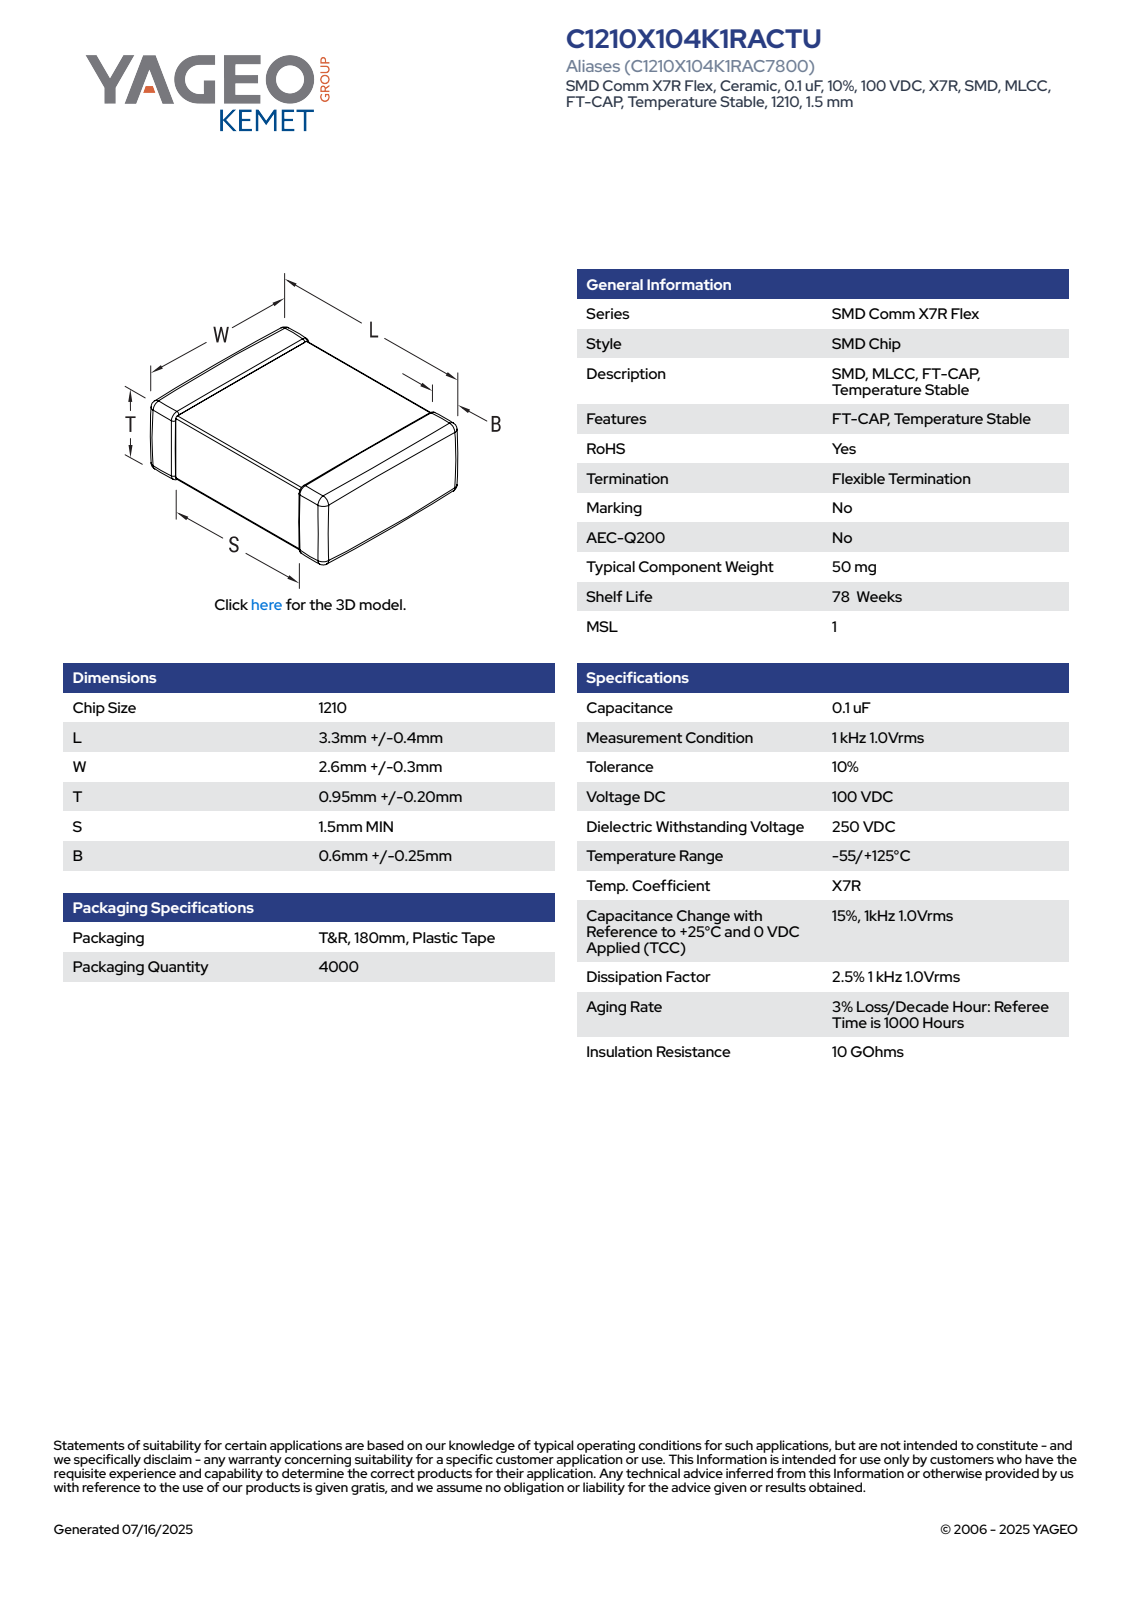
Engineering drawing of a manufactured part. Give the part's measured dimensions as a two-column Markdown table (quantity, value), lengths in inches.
| quantity | value |
| --- | --- |
| part name | CCS_CCSTD_1210_L3.7W2.9T1.15B0.6 |
| STEP written by | SolidWorks 2021 (AUTOMOTIVE_DESIGN) |
| units | inches |
| bodies | 4 solids, 125 faces (71 planar, 38 cylindrical, 16 other) |
| overall size | 0.146 × 0.114 × 0.045 |
| volume | 0.001 in³ |
| surface area | 0.057 in² |
| main face-to-face distances | 0.043, 0.041, 0.045, 0.112, 0.146, 0.109, 0.114, 0.017, 0.062, 0.084 |
